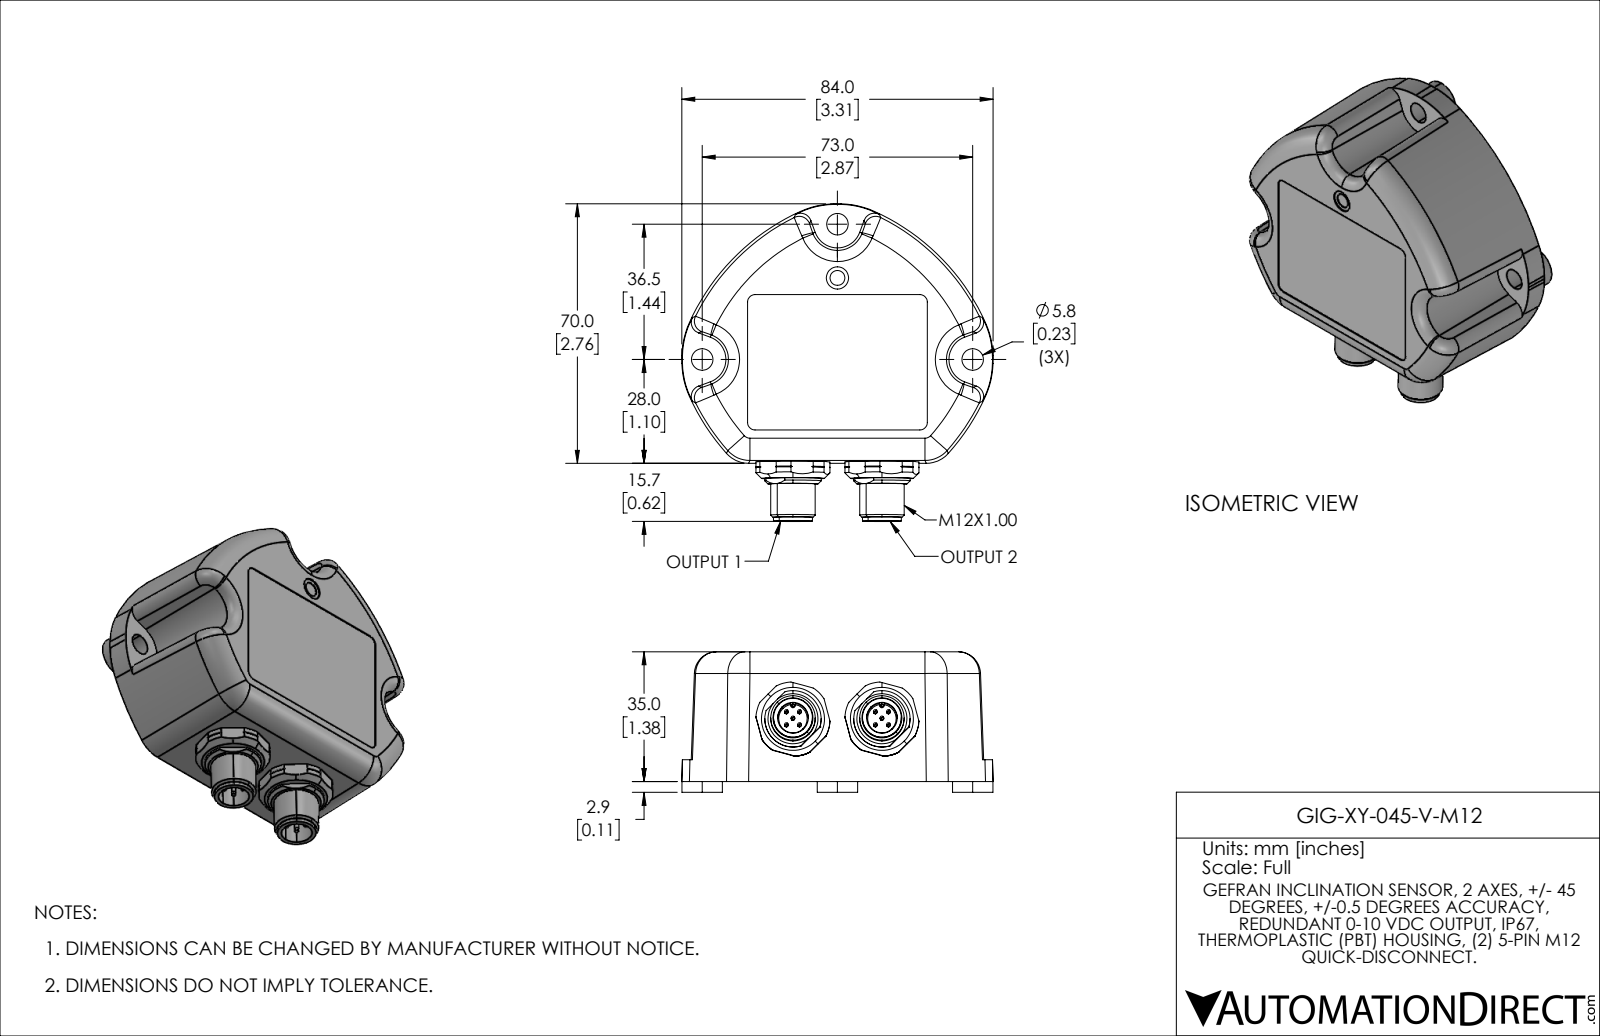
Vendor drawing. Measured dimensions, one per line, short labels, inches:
name: GIG-XY-045-V-M12
written by: SolidWorks 2021 (AUTOMOTIVE_DESIGN)
unit: in
bodies: 1 solid, 365 faces (87 planar, 123 cylindrical, 155 other)
size: 3.374 × 3.307 × 1.492
volume: 9.029 in³; area: 32.38 in²
holes: 3× ⌀0.228, 2× ⌀0.327, 1× ⌀0.157, 1× ⌀0.236
bosses: 10× ⌀0.039, 3× ⌀0.429, 2× ⌀0.472, 2× ⌀0.413
rounds: 4× R0.02, 4× R0.079, 3× R0.299, 2× R0.024, 2× R0.273, 2× R0.394, 1× R0.236, 1× R0.301
face distances: 1.37, 1.378, 0.232, 1.138, 1.146, 0.114, 0.346, 1.484, 1.492, 0.668
hole spacings: 1.678, 2.032, 0.571, 0.945, 2.874
